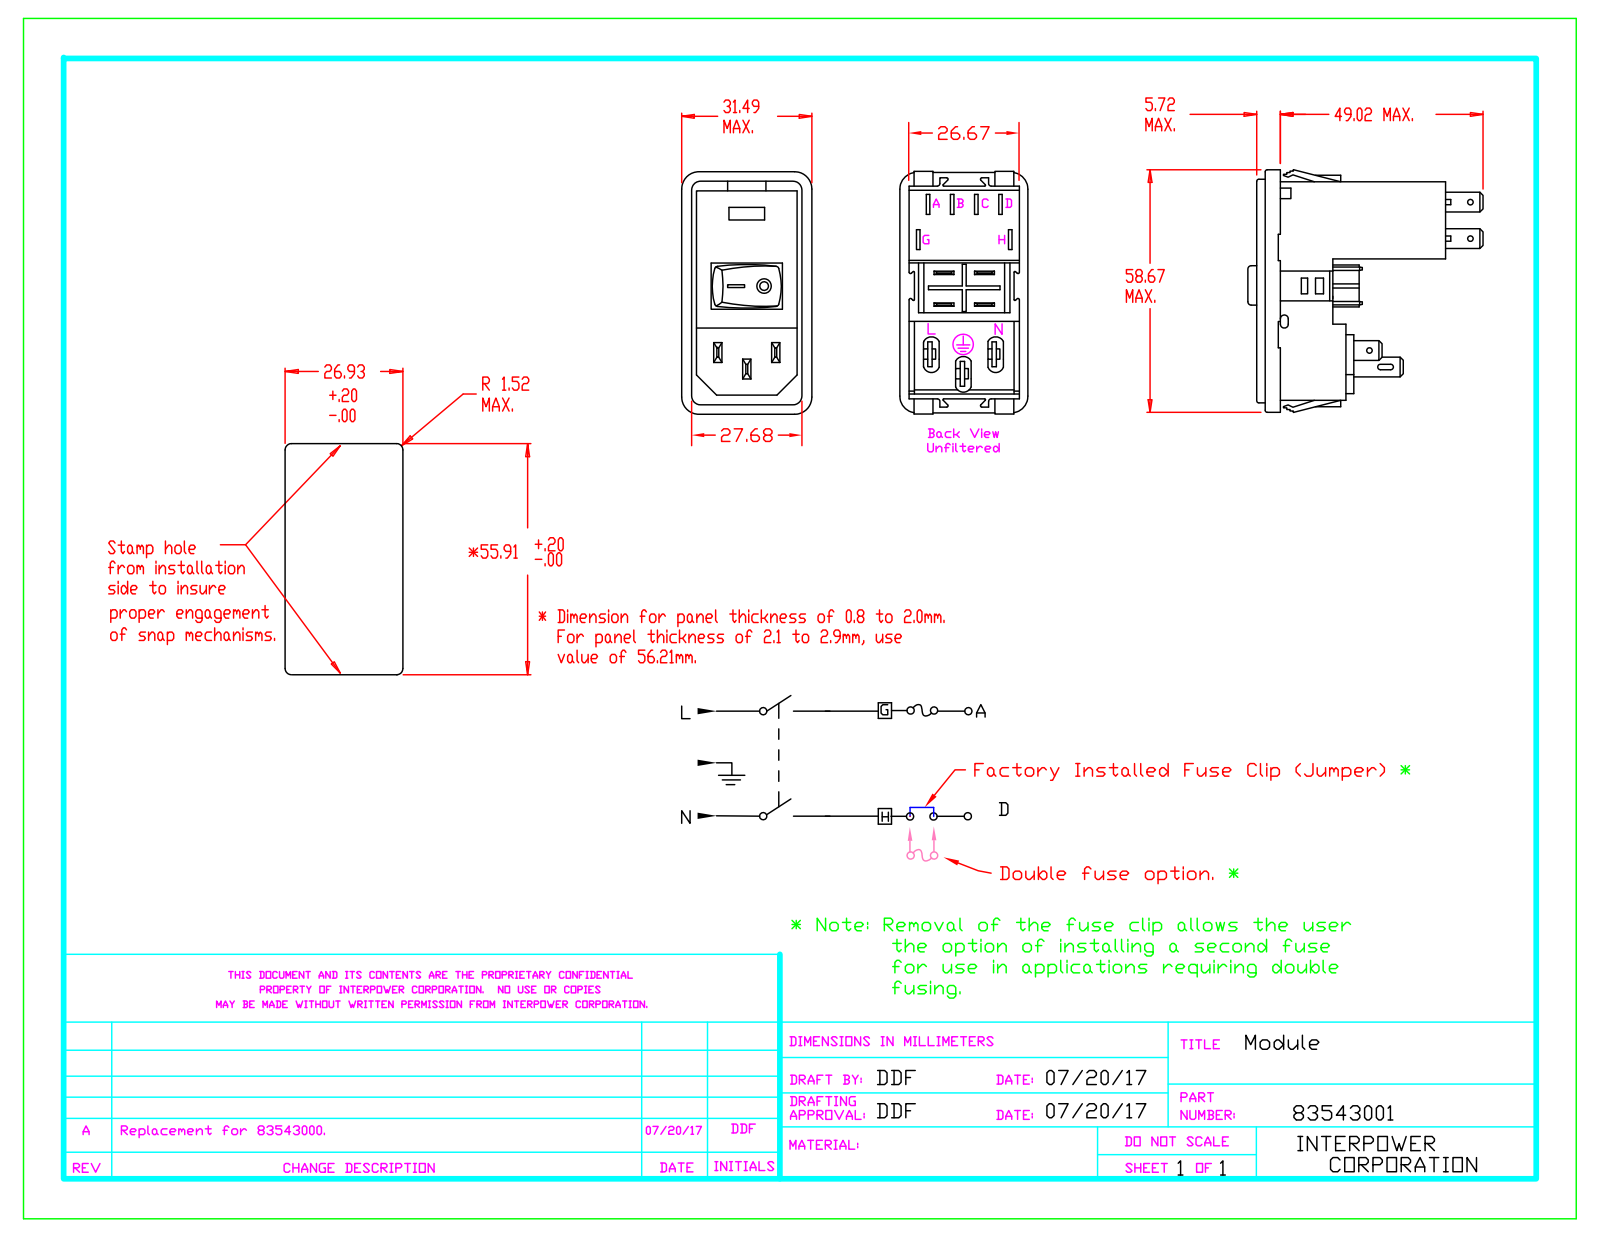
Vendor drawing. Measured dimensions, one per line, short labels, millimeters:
name: 83543000-R1
written by: SolidWorks 2007 (CONFIG_CONTROL_DESIGN)
unit: mm
bodies: 1 solid, 595 faces (461 planar, 83 cylindrical, 51 other)
size: 59.52 × 56.71 × 31.49
volume: 35 595 mm³; area: 16 230 mm²
holes: 5× ⌀1.33, 1× ⌀2.25, 1× ⌀3.5
bosses: 1× ⌀2.87, 1× ⌀2.75
rounds: 19× R1, 8× R0.51, 5× R0.25, 4× R2.16, 4× R4.19, 2× R0.67, 2× R0.76, 1× R0.88
face distances: 26, 18.65, 0.48, 12.7, 5.71, 16.25, 39.96, 45.67, 34.9, 25.74
hole spacings: 8.82, 10.6, 36.48, 43.43
